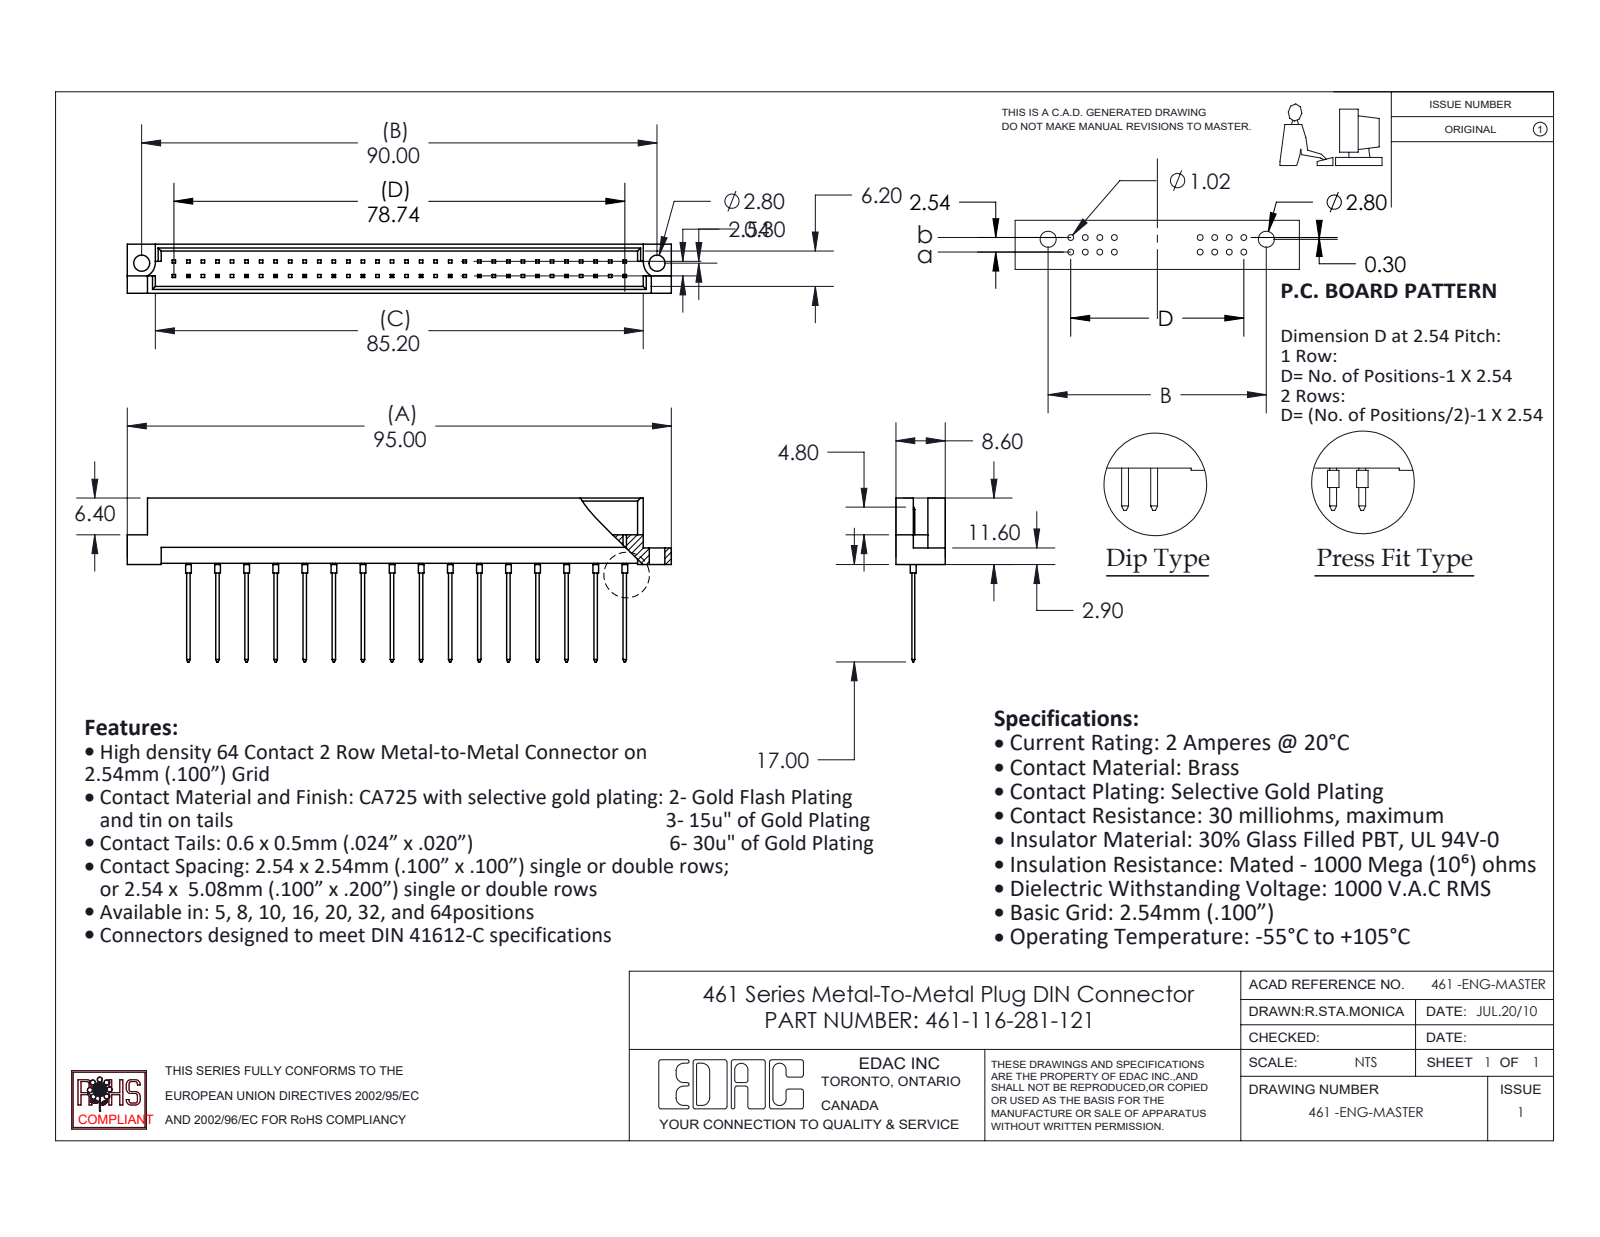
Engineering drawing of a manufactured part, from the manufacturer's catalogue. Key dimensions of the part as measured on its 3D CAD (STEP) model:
Part name (STEP PRODUCT): 461 Part_64; 461-116-281-121; 461-290_81
STEP written by: SolidWorks 2020 (CONFIG_CONTROL_DESIGN)
Units: millimetres
Bodies: 17 solids, 657 faces (618 planar, 39 cylindrical, 0 other)
Overall size (bounding box): 95 × 28.6 × 8.6
Volume: 4 796 mm³ · Surface area: 6 654 mm²
Round holes (diameter × count): ⌀2.8 ×2
Round bosses / shafts (diameter × count): ⌀1 ×16
Partial cylindrical surfaces — rounded edges, fillets, slot ends (radius × count): R2.8 ×2
Main face-to-face distances: 1.2, 7.4, 8.6, 6.2, 5, 3.28, 5.32, 2.08, 4.12, 2.78
Hole centre spacings: 90
